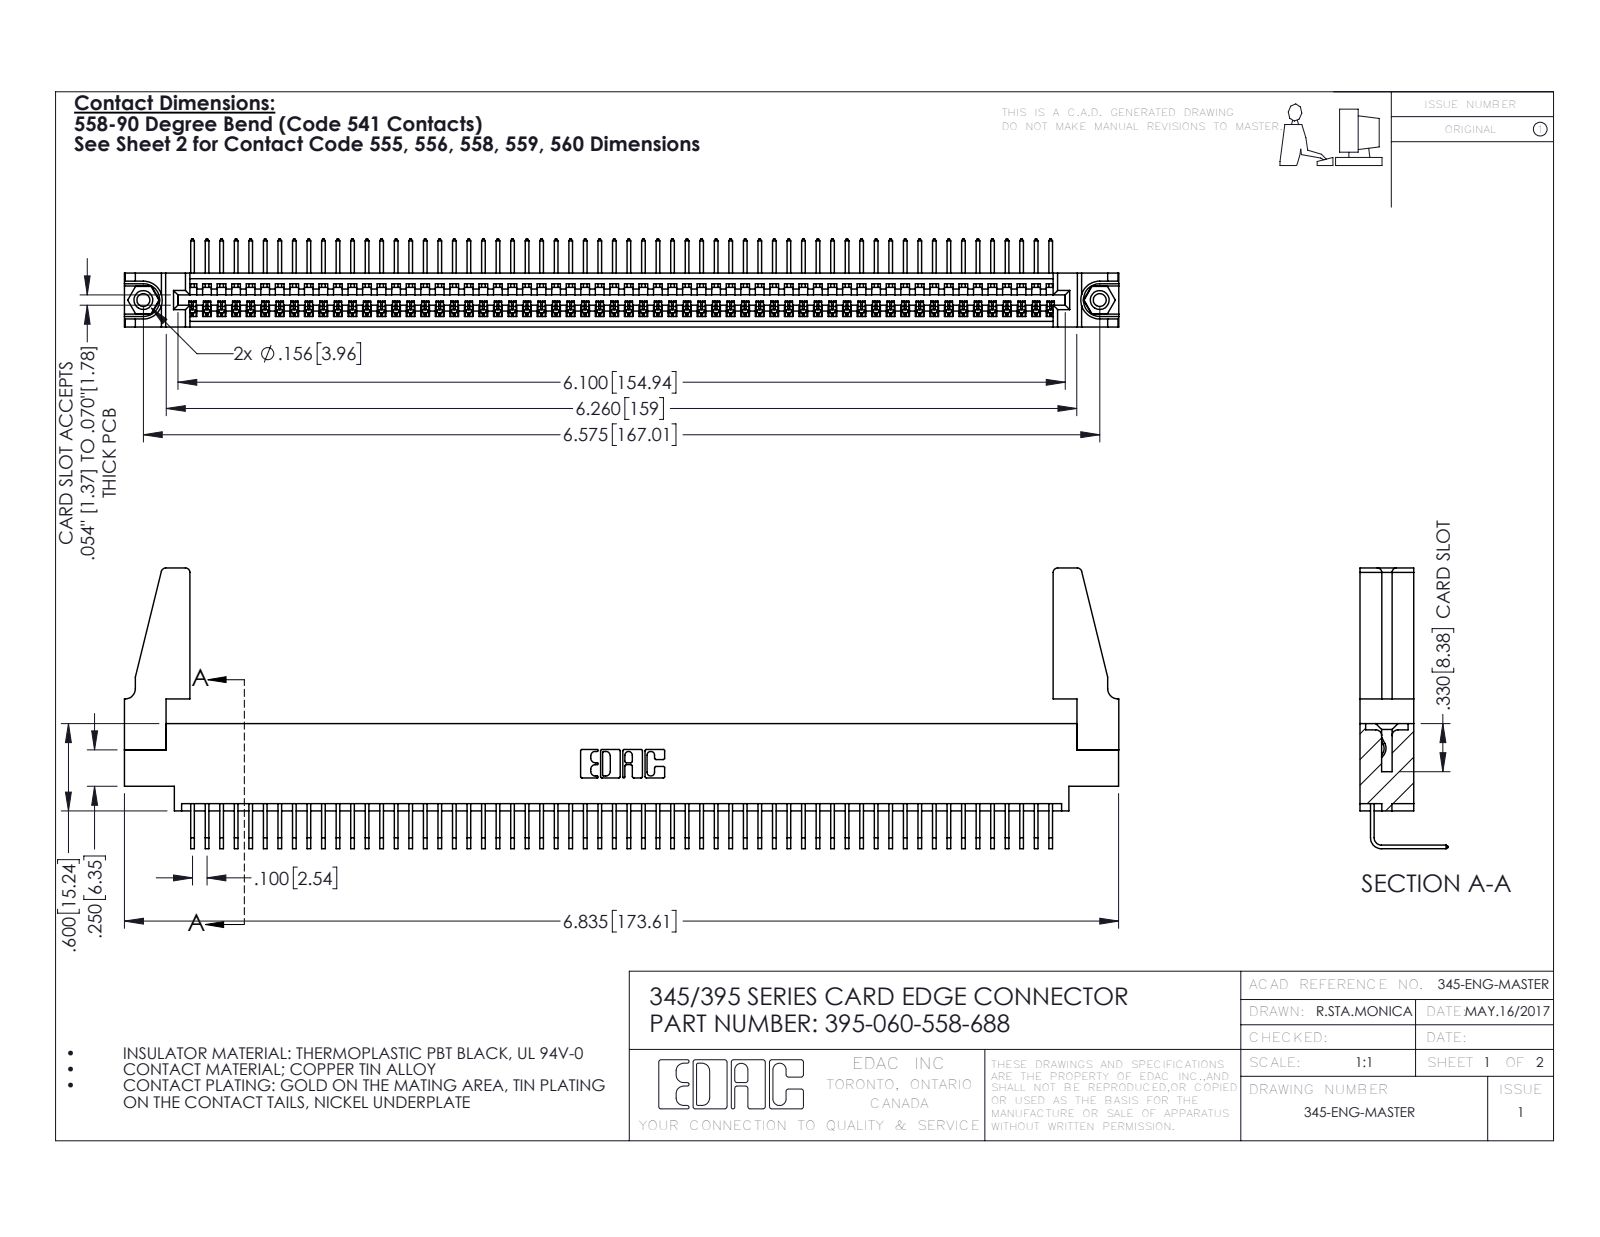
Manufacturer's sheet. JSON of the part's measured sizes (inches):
{"part_name": "395-060-558-688; 345-292-001_558 Tail - 2; 345 Part_0.170 Offset - 0.156 Dia-TH; 345-220-078_345-220-088 (+1 more)", "step_written_by": "SolidWorks 2016 (CONFIG_CONTROL_DESIGN)", "units": "inches", "bodies": {"solids": 65, "faces": 3854, "planar": 2676, "cylindrical": 1162, "other": 16}, "overall_size": [6.836, 1.929, 0.605], "volume_in3": 1.219, "surface_area_in2": 41.7, "round_holes": [[0.089, 2], [0.125, 2], [0.156, 2], [0.064, 1]], "round_bosses_or_shafts": [[0.155, 2]], "partial_cylinders_radius": [[0.006, 120], [0.01, 22], [0.03, 8], [0.007, 6], [0.031, 6], [0.026, 3], [0.031, 2], [0.04, 2]], "face_to_face_distances": [0.072, 0.298, 0.37, 0.098, 0.272, 0.025, 0.2, 0.225, 0.175, 0.149], "hole_center_spacings": [0.27, 6.339, 6.575]}
